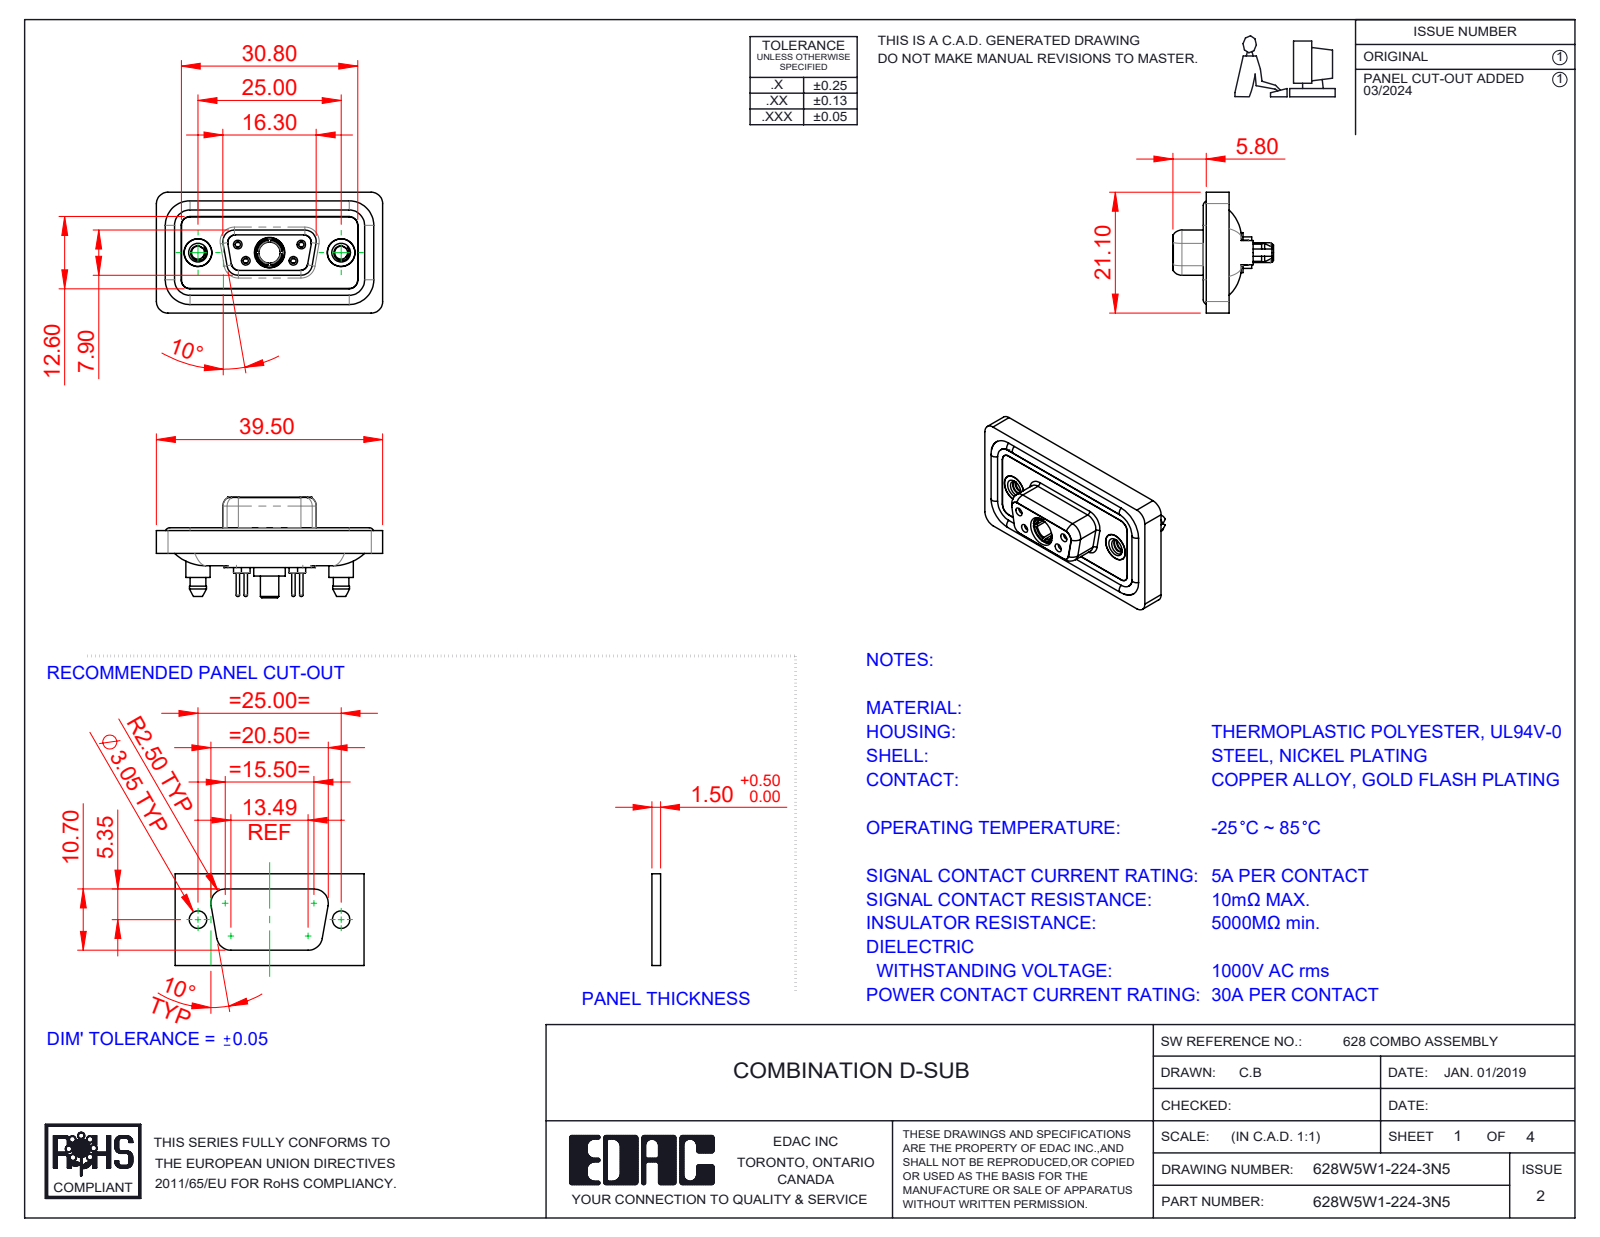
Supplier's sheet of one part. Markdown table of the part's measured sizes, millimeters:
| quantity | value |
| --- | --- |
| part name | 628Combo Contact Row 2_24; 628Combo Shell Front_09 Contacts; 628Combo Shell Rear_09 Contacts; Power Socket_30A S (+5 more) |
| STEP written by | SolidWorks 2023 (CONFIG_CONTROL_DESIGN) |
| units | millimeters |
| bodies | 13 solids, 730 faces (210 planar, 319 cylindrical, 201 other) |
| overall size | 39.5 × 21.1 × 17.55 |
| volume | 4 908 mm³ |
| surface area | 7 973 mm² |
| round holes (diameter × count) | 0.9 × 4, 1.1 × 4, 1.5 × 4, 2 × 4, 4.85 × 3, 1.6 × 2, 1.7 × 2, 2.26 × 2, 4 × 2, 4.05 × 2, 5 × 2, 3.7 × 1 |
| round bosses / shafts (diameter × count) | 1.6 × 6, 2.2 × 4, 0.6 × 4, 5.4 × 2, 4.95 × 2, 4.8 × 2, 4.25 × 2, 5.5 × 1 |
| partial cylindrical surfaces (radius × count) | 1.5 × 24, 2 × 18, 1.6 × 10, 1.35 × 8, 0.25 × 4, 0.5 × 4, 0.6 × 4, 0.65 × 4 |
| main face-to-face distances | 0.4, 2.9, 1.1, 1.8, 1.6, 0.5, 5.65, 7.45, 5.35, 3.6 |
| hole center spacings | 3.16, 5.72, 7.1, 12.5, 18.1, 4.39, 4.4, 8.31 |
